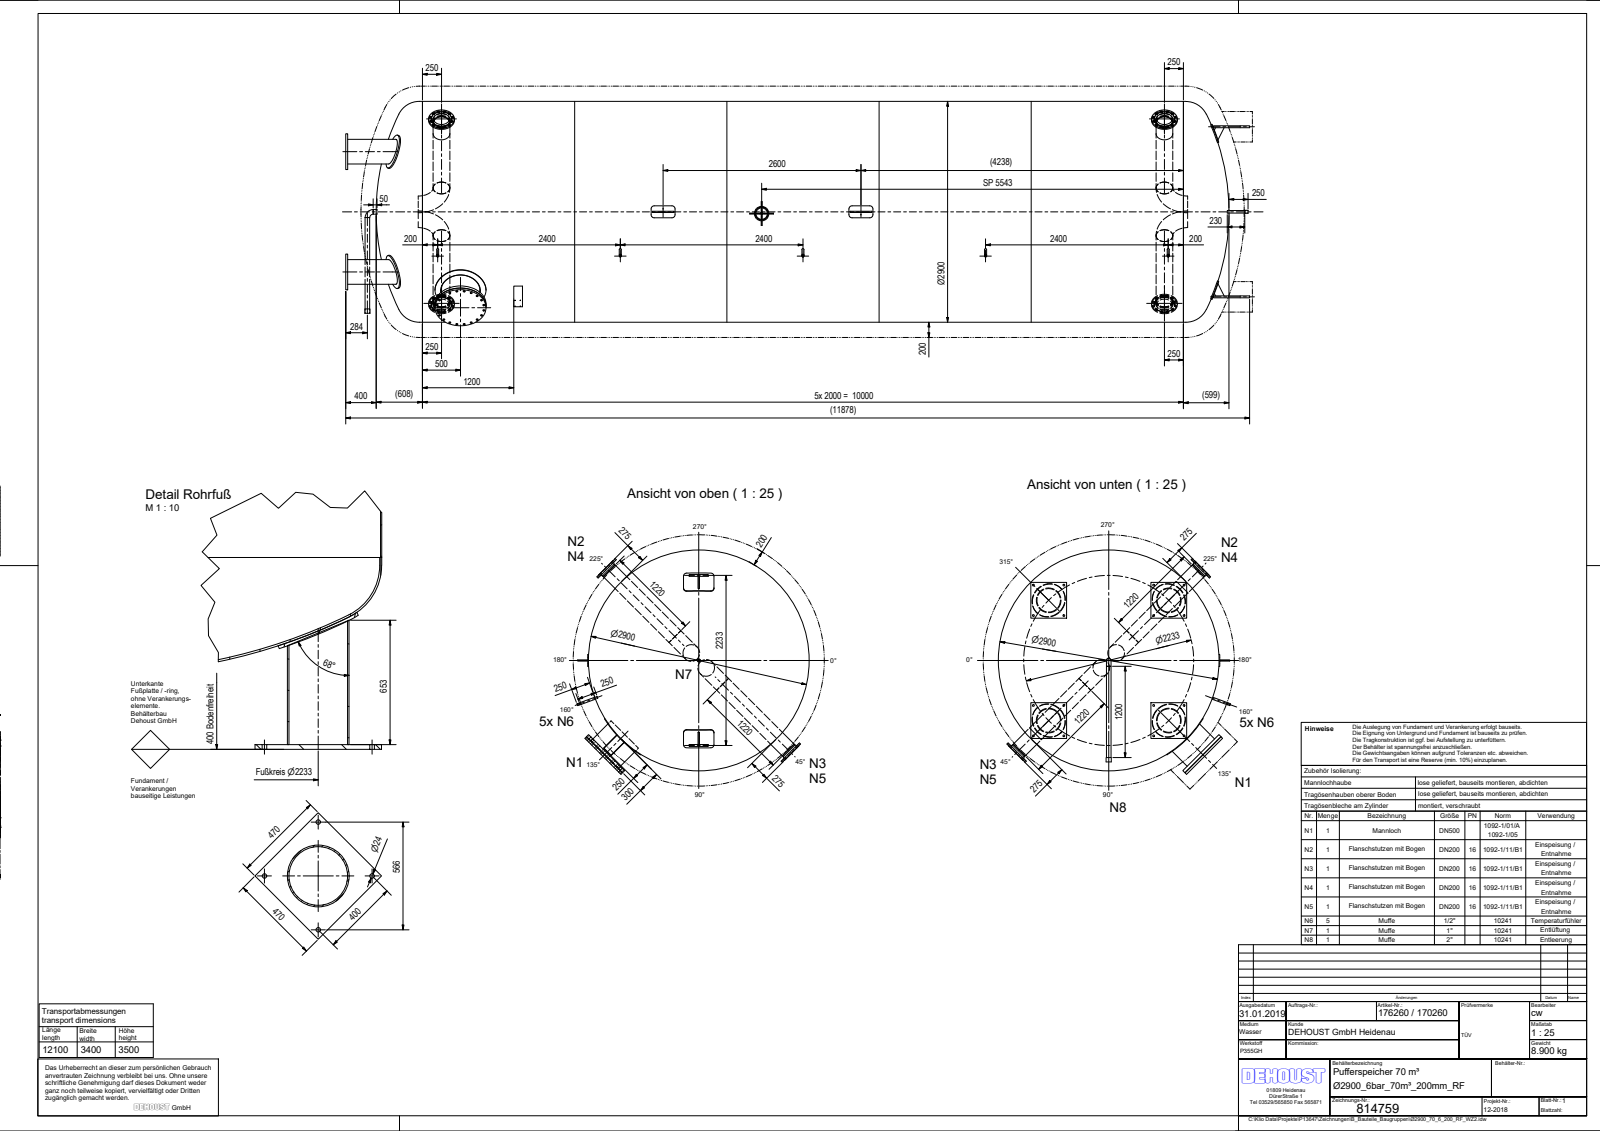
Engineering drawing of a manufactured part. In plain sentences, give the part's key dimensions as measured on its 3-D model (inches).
The part is named "Ø2900_70_6_200_RF_WZ2; Klöpper_Gew_Ø2900_8,3; Klöpper_Gew_Ø2900_10,3; Zyl_Ø2900_6x10000_mV_2019 (+8 more)". Its 3-D file was written by "Autodesk Inventor 2019 (AUTOMOTIVE_DESIGN)". It is 59 solids with 469 faces: 178 planar, 245 cylindrical and 46 other. Overall it measures 467.642 by 120.157 by 115.994 inches. Its volume is 64 320 cubic inches and its surface area 373 900 square inches. Round holes: 48 of diameter 0.866, 36 of diameter 1.024, 16 of diameter 0.945, 5 of diameter 0.733, 5 of diameter 0.854, 5 of diameter 1.059, 4 of diameter 0.228, 4 of diameter 8.067, 4 of diameter 8.161, 4 of diameter 8.626, 4 of diameter 12.122, 2 of diameter 0.197. Round bosses or shafts: 8 of diameter 8.626, 5 of diameter 1.059, 5 of diameter 1.039, 4 of diameter 17.717, 4 of diameter 13.386, 4 of diameter 12.752, 4 of diameter 10.551, 2 of diameter 26.378. Partial cylindrical surfaces (rounded edges, fillets, slot ends): 16 of radius 1.654, 6 of radius 0.394, 4 of radius 0.236, 2 of radius 0.197, 2 of radius 1.417, 2 of radius 2.835, 1 of radius 4.921, 1 of radius 57.323. The main face-to-face distances are 0.984, 23.622, 223.935, 249.132, 222.951, 248.148, 25.197, 1.102, 184.252, 209.449. The hole center spacings are 12.205, 5.807, 7.543, 94.488, 19.748, 188.976, 17.26, 10.058.
